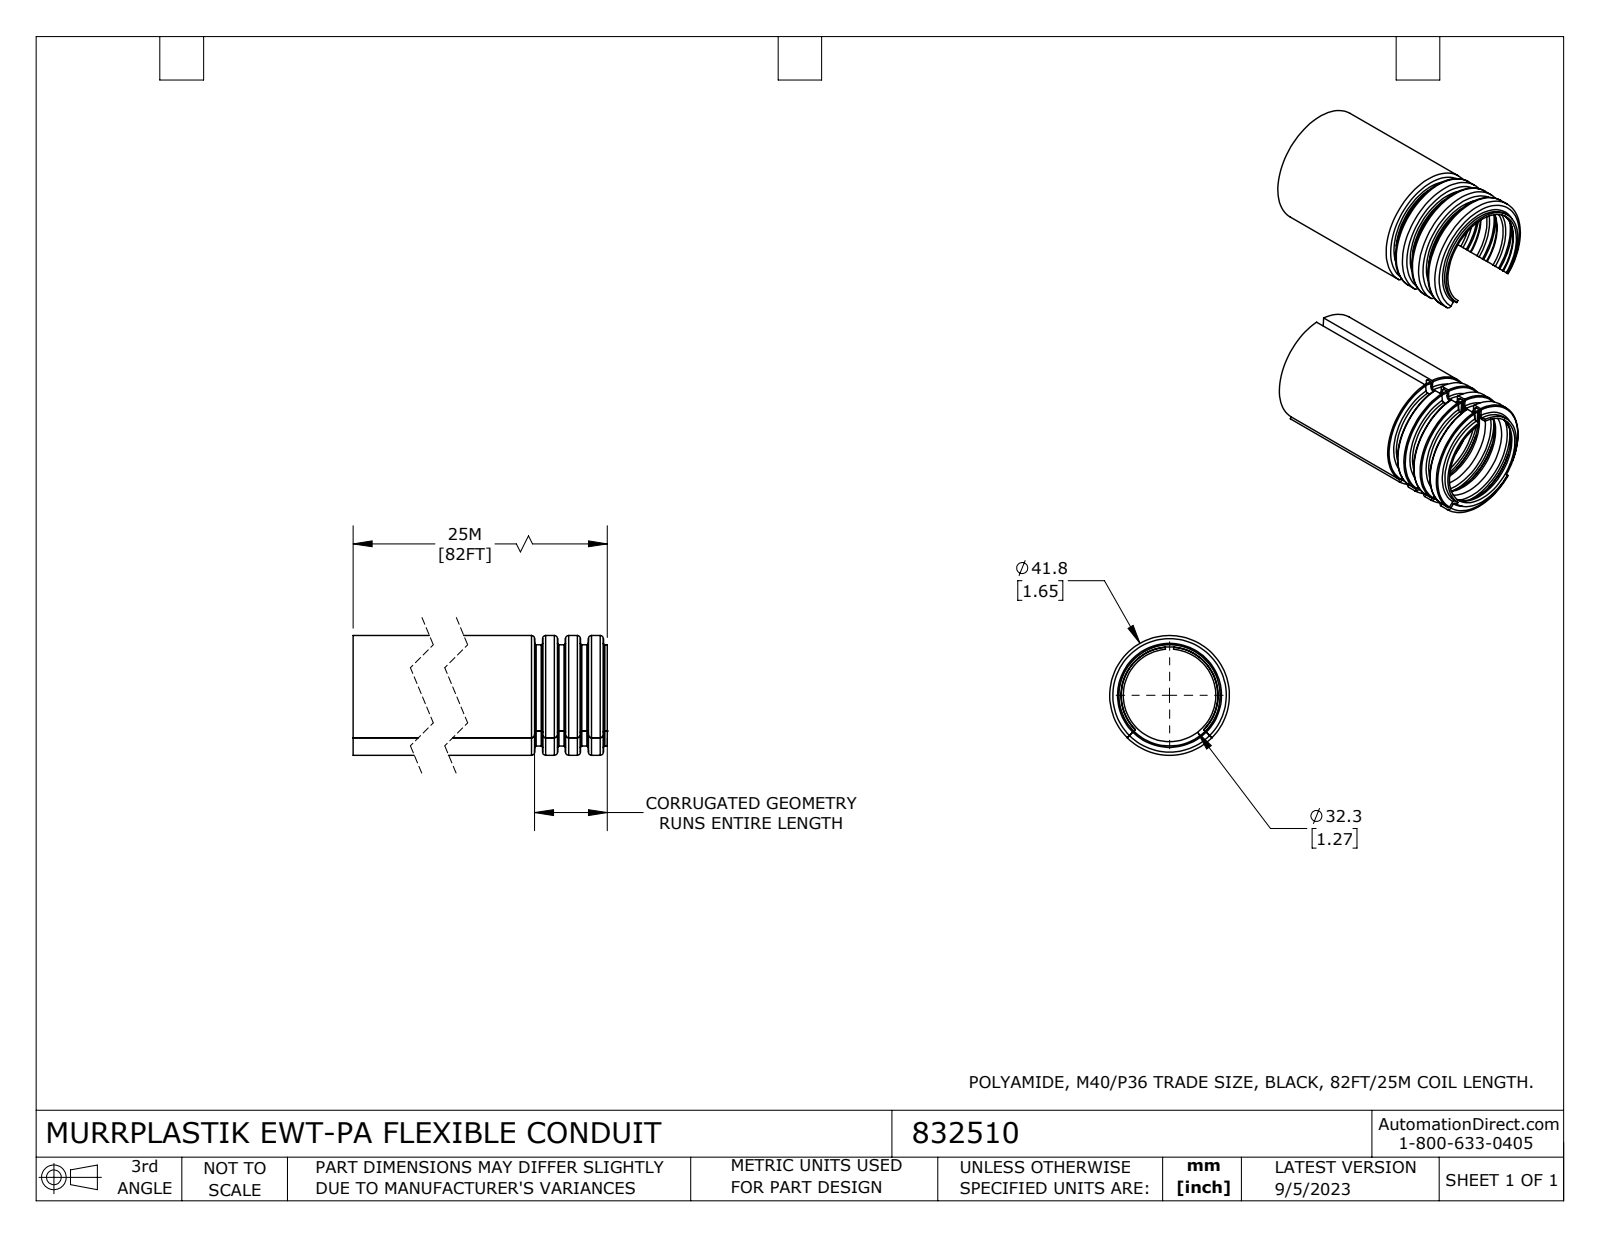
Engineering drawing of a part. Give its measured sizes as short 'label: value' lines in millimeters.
name: 832510
written by: SolidWorks 2021 (CONFIG_CONTROL_DESIGN)
unit: mm
bodies: 2 solids, 335 faces (10 planar, 107 cylindrical, 218 other)
size: 80 × 41.8 × 41.8
volume: 35 900 mm³; area: 41 970 mm²
holes: 1× ⌀32.3, 1× ⌀38.8
bosses: 1× ⌀41.8, 1× ⌀35.3
rounds: 1× R16.9, 1× R20.1
face distances: 80
